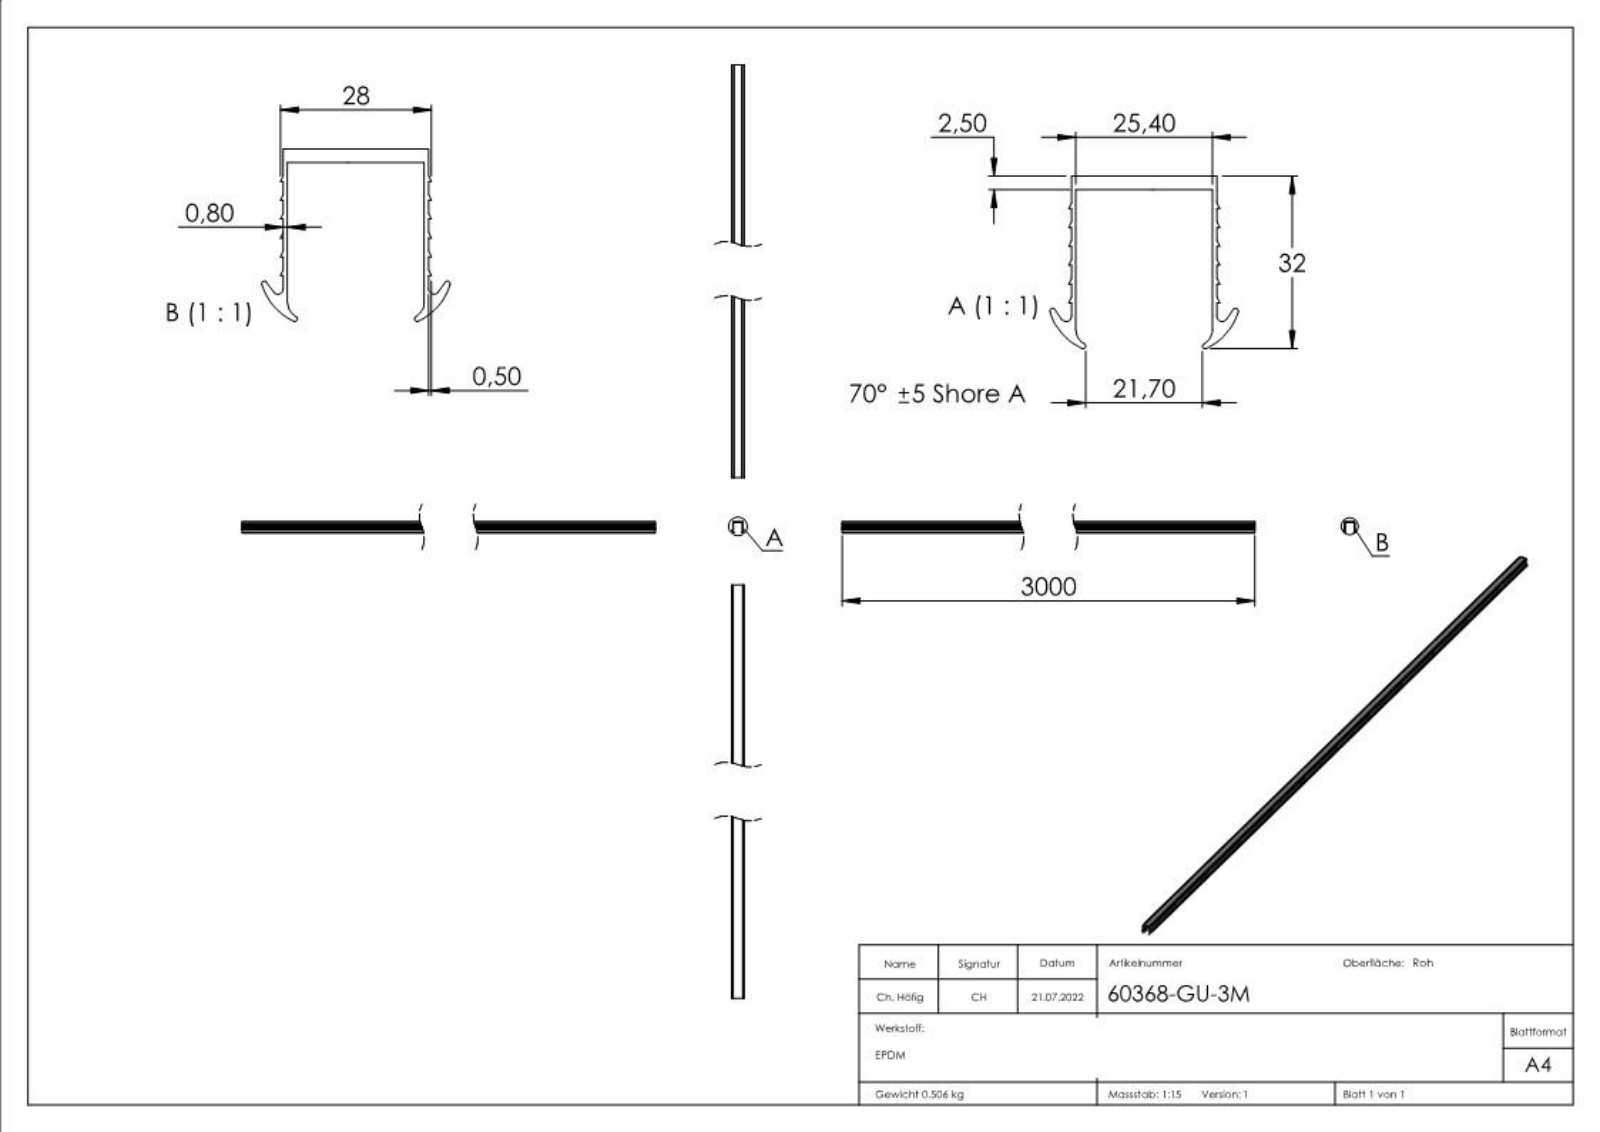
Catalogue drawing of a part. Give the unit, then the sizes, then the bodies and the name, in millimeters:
Units: millimetres
Overall size (bounding box): 3000 × 35 × 32
Partial cylindrical surfaces — rounded edges, fillets, slot ends (radius × count): R0.5 ×4, R1 ×2, R3 ×2, R11 ×2
Main face-to-face distances: 0.8, 26.2, 25.4, 2.5, 27, 1.48, 3.5, 7, 2.97, 4.45
Volume: 428 782 mm³ · Surface area: 612 123 mm²
Bodies: 1 solid, 359 faces (193 planar, 10 cylindrical, 156 other)
Part name (STEP PRODUCT): 60368-GU-3M
STEP written by: SolidWorks 2018 (CONFIG_CONTROL_DESIGN)
